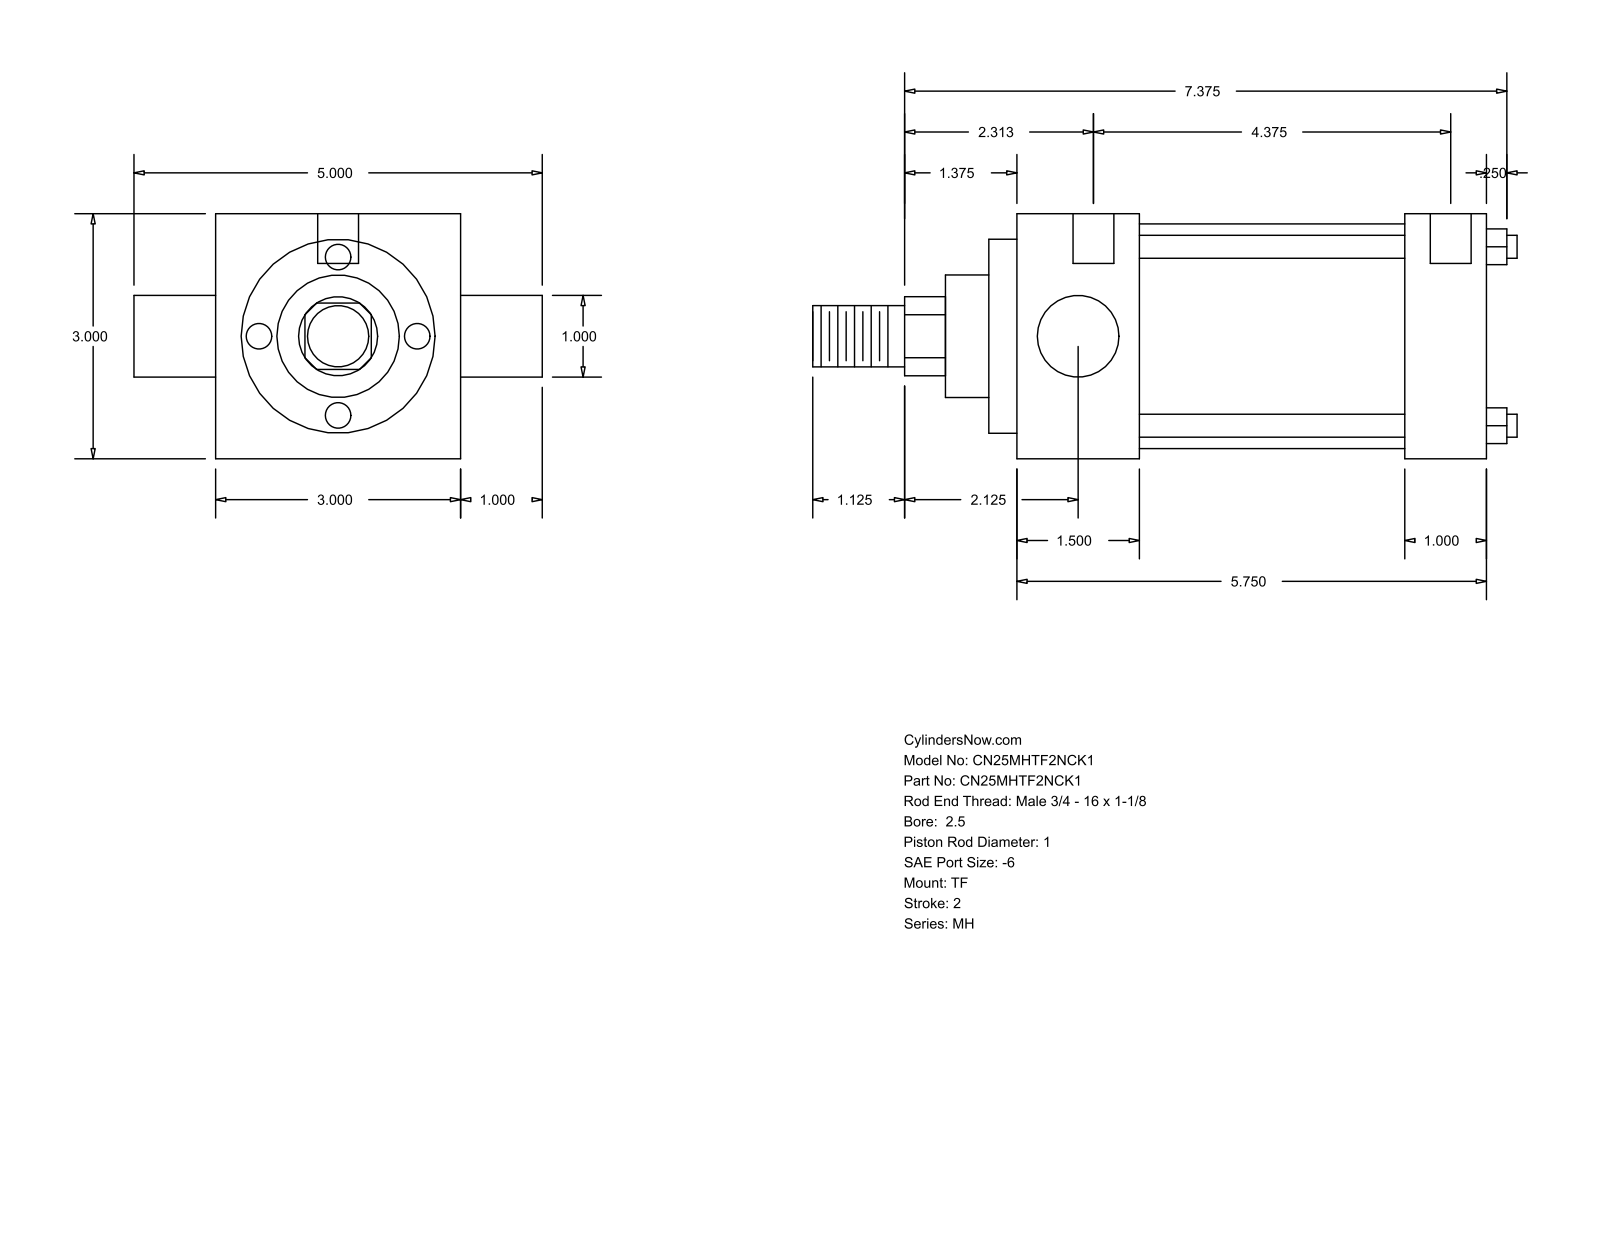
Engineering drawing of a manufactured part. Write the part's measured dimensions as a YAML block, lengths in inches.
part_name: "MH_TF__0250_1"
step_written_by: "GSSL Pune (CONFIG_CONTROL_DESIGN)"
units: inches
bodies: {solids: 0, faces: 86, planar: 61, cylindrical: 25, other: 0}
overall_size: [8.625, 5, 3]
round_holes:
  - {diameter: 0.219, count: 3}
  - {diameter: 0.5, count: 2}
round_bosses_or_shafts:
  - {diameter: 0.281, count: 4}
  - {diameter: 1, count: 2}
  - {diameter: 2.75, count: 1}
  - {diameter: 2.375, count: 1}
  - {diameter: 1.5, count: 1}
  - {diameter: 0.75, count: 1}
partial_cylinders:
  - {radius: 0.484, count: 1}
face_to_face_distances: [3, 5.75, 1, 1.5, 4.25, 4.75, 3.25, 0.344, 1.844, 5.094]
hole_center_spacings: [0.125, 0.187, 4.375, 4.5, 4.562, 4.687]
